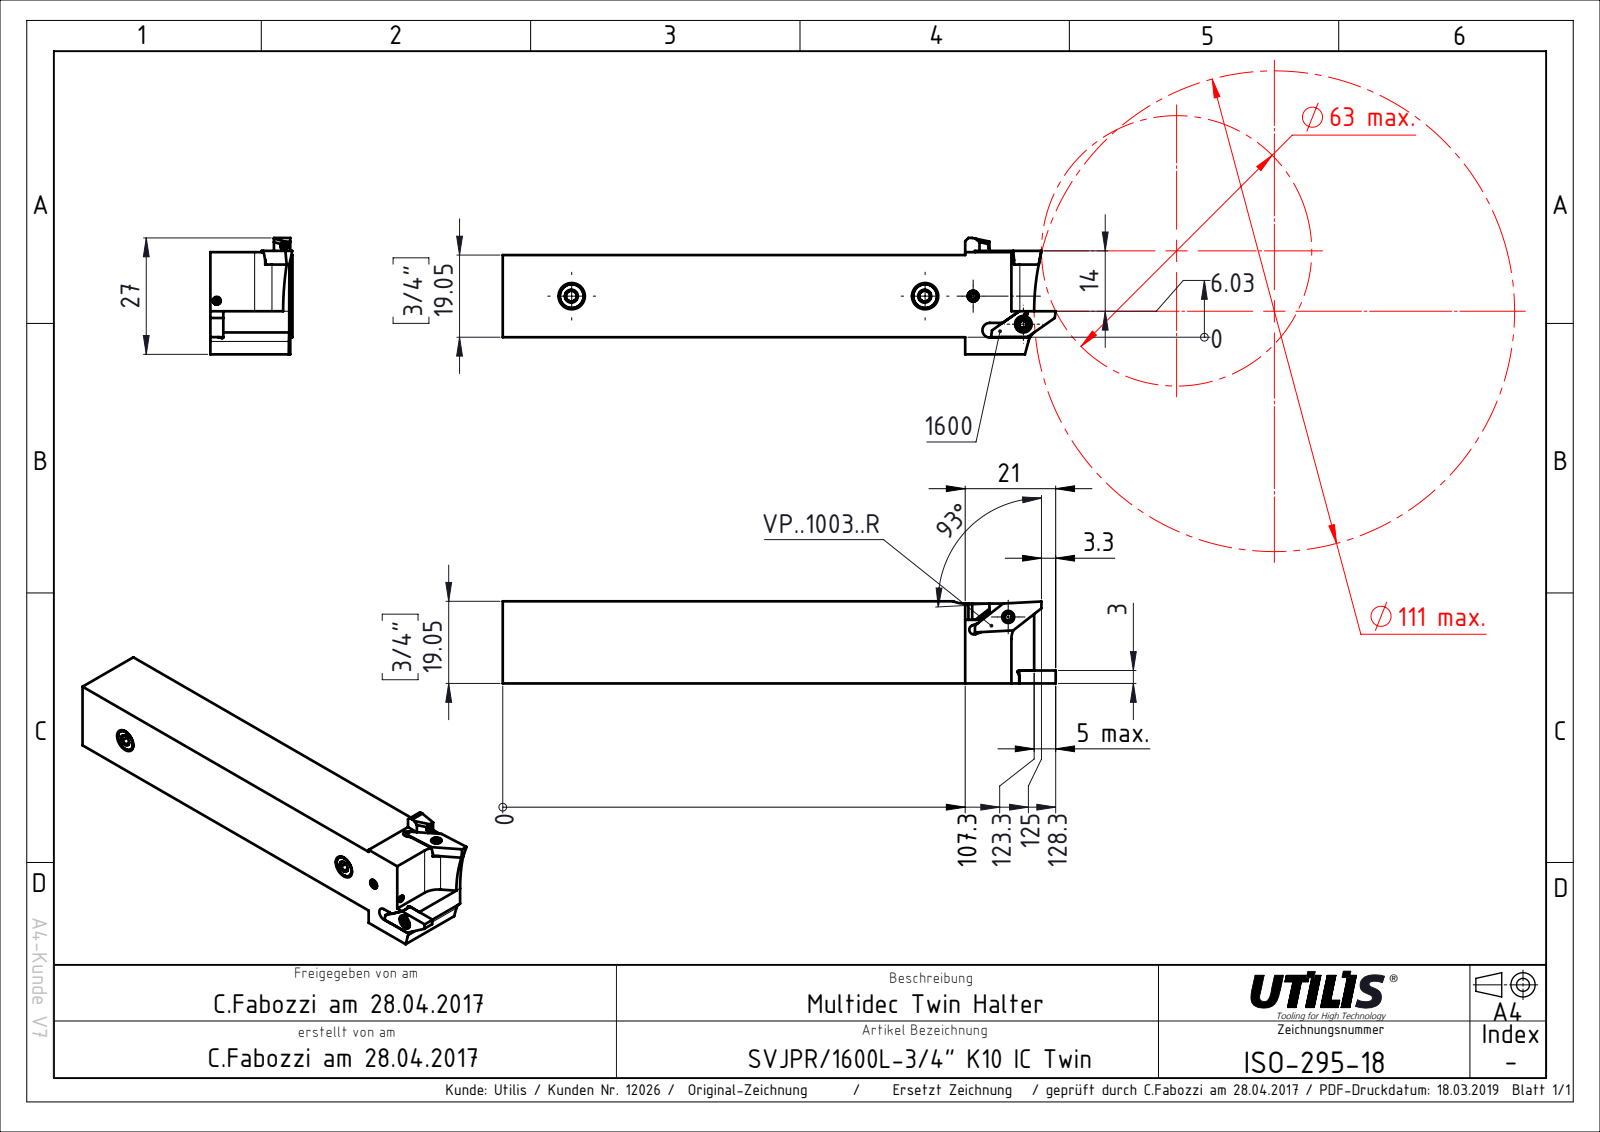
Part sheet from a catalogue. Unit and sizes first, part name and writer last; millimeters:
Units: millimetres
Overall size (bounding box): 128.3 × 27 × 19.05
Partial cylindrical surfaces — rounded edges, fillets, slot ends (radius × count): R0.25 ×2, R6.1 ×2, R0.5 ×1, R1.1 ×1, R1.55 ×1, R1.7 ×1, R4.1 ×1, R5.1 ×1
Main face-to-face distances: 19.06, 3.97, 23.03, 118.02, 23.7, 19.73, 0.67, 10.72, 107.3, 10
Volume: 44 886 mm³ · Surface area: 10 632 mm²
Bodies: 1 solid, 81 faces (67 planar, 12 cylindrical, 2 other)
Part name (STEP PRODUCT): ISO-295-18
STEP written by: SolidWorks 2016 (AUTOMOTIVE_DESIGN)
